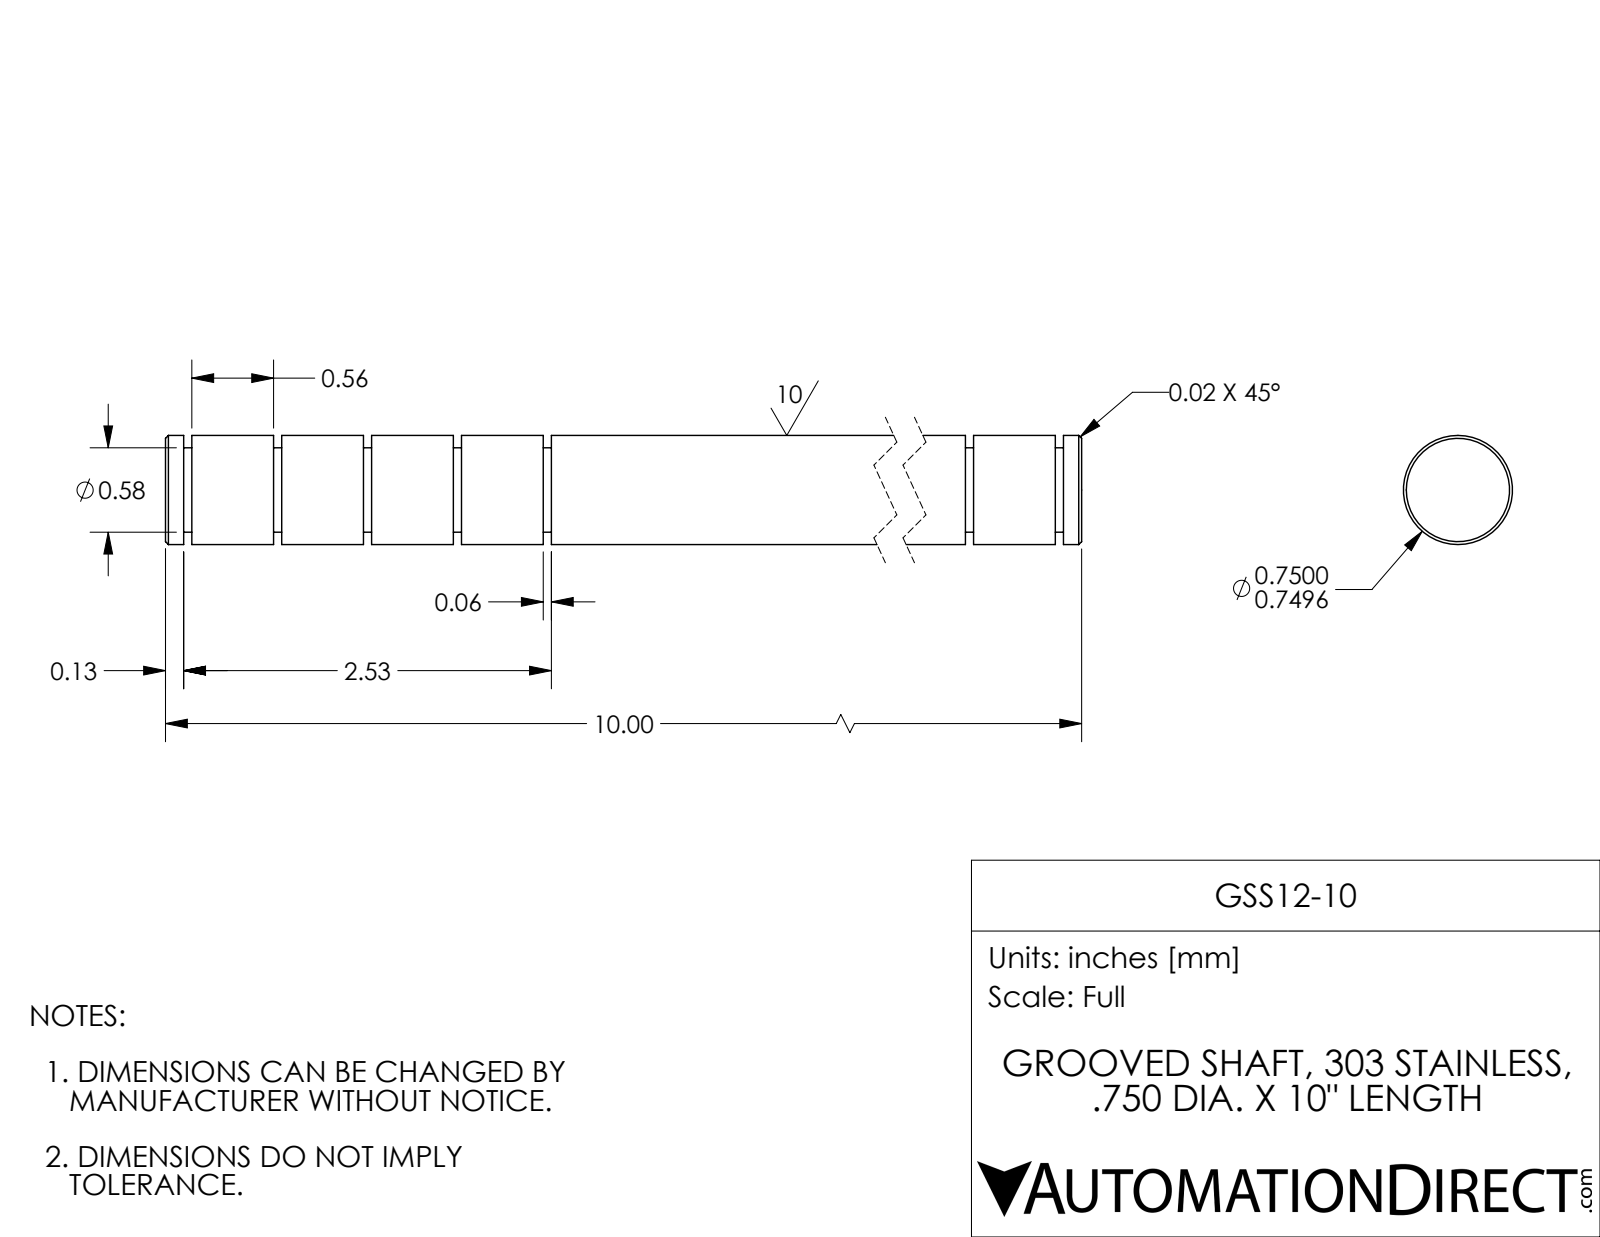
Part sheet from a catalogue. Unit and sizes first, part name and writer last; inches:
Units: inches
Overall size (bounding box): 10 × 0.75 × 0.75
Round bosses / shafts (diameter × count): ⌀0.75 ×1, ⌀0.58 ×1
Main face-to-face distances: 0.618, 0.056, 0.674, 1.236, 0.618, 1.292, 0.562, 9.076, 7.222, 10
Volume: 4.347 in³ · Surface area: 26.67 in²
Bodies: 1 solid, 50 faces (16 planar, 30 cylindrical, 4 other)
Part name (STEP PRODUCT): GSS12-10
STEP written by: SolidWorks 2017 (AUTOMOTIVE_DESIGN)
